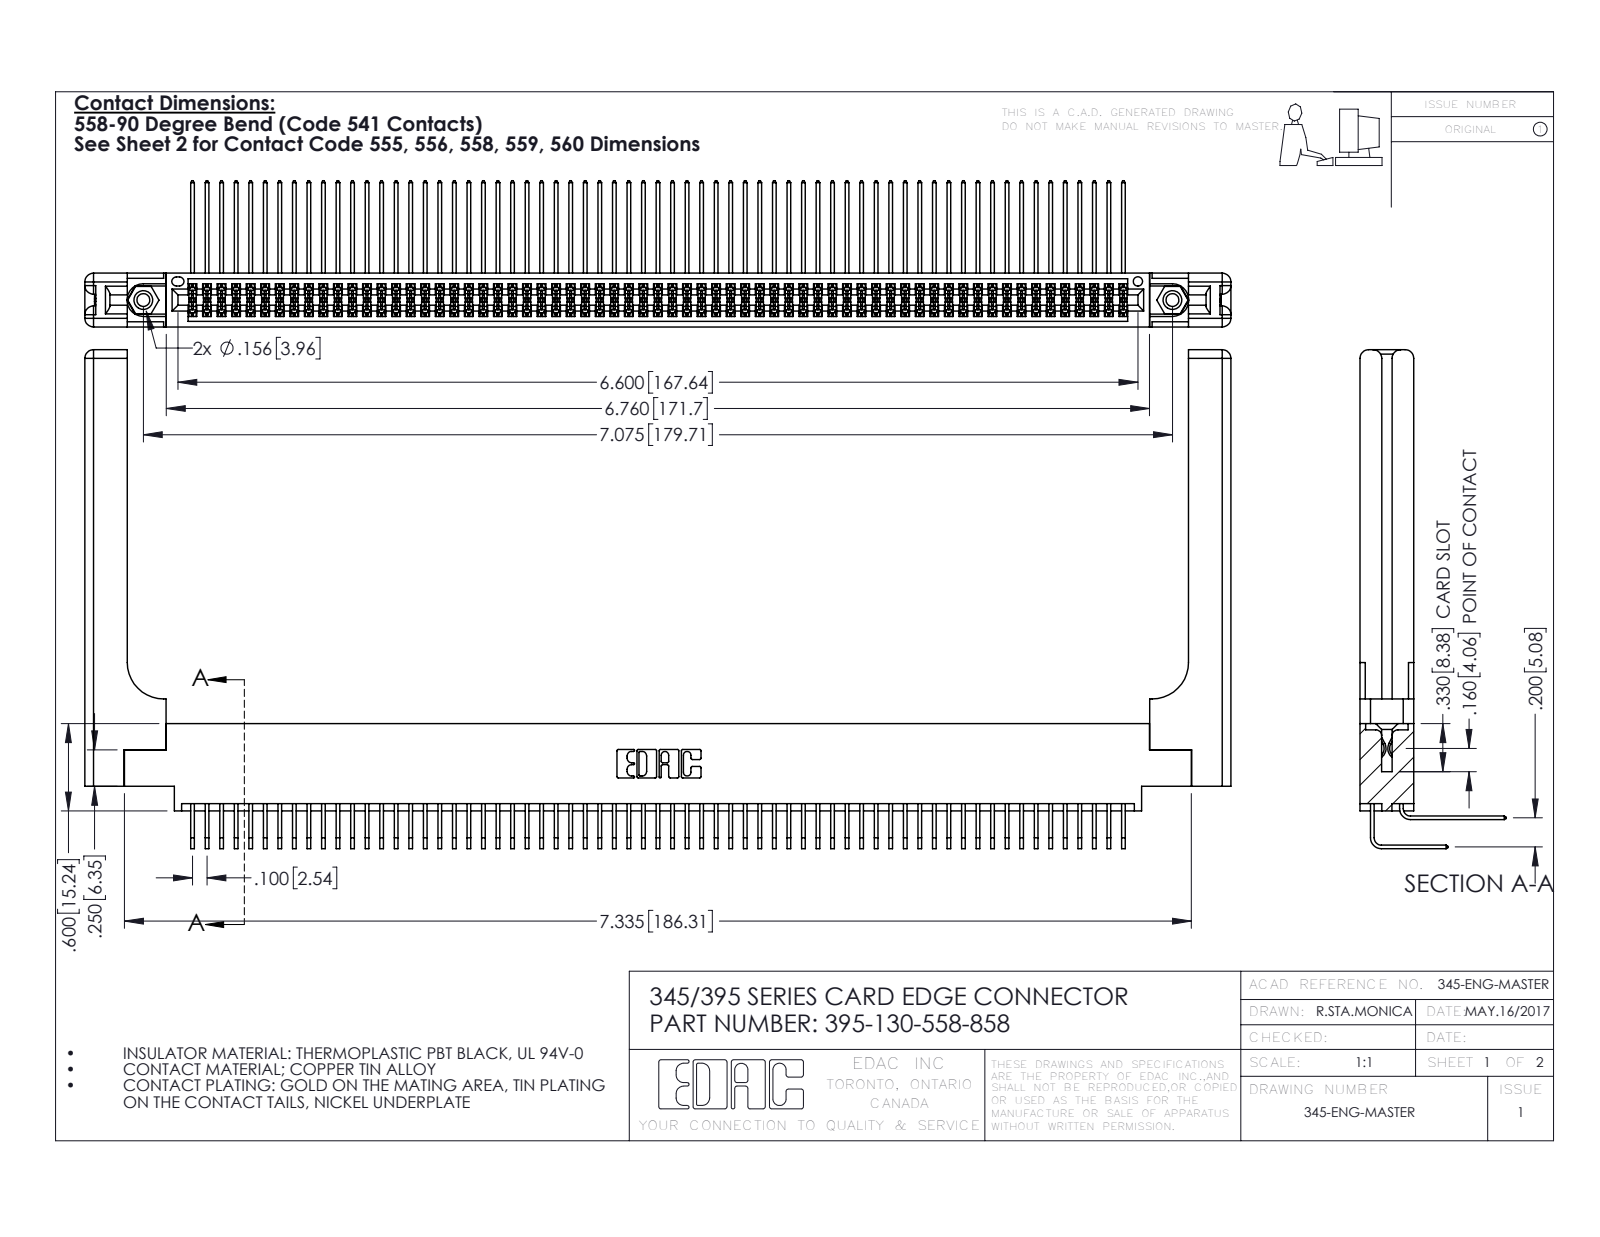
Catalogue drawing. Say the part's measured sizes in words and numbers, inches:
The part is named "395-130-558-858; 345-292-001_558 559 Tail - 1; 345-220-058_345-220-058; 345 Part_0.170 Offset - 0.156 Dia-TH (+2 more)". Its 3-D file was written by "SolidWorks 2016 (CONFIG_CONTROL_DESIGN)". It is 135 solids with 7146 faces: 4782 planar, 2304 cylindrical and 60 other. Overall it measures 7.879 by 3.429 by 1.005 inches. Its volume is 1.755 cubic inches and its surface area 60.71 square inches. Round holes: 2 of diameter 0.089, 2 of diameter 0.125, 2 of diameter 0.156, 1 of diameter 0.064. Round bosses or shafts: 2 of diameter 0.155. Partial cylindrical surfaces (rounded edges, fillets, slot ends): 196 of radius 0.006, 22 of radius 0.01, 16 of radius 0.06, 6 of radius 0.007, 6 of radius 0.031, 3 of radius 0.026, 2 of radius 0.014, 2 of radius 0.019. The main face-to-face distances are 0.072, 0.298, 0.37, 0.2, 0.098, 0.272, 0.025, 0.225, 0.175, 0.025. The hole center spacings are 0.27, 6.839, 7.075.
